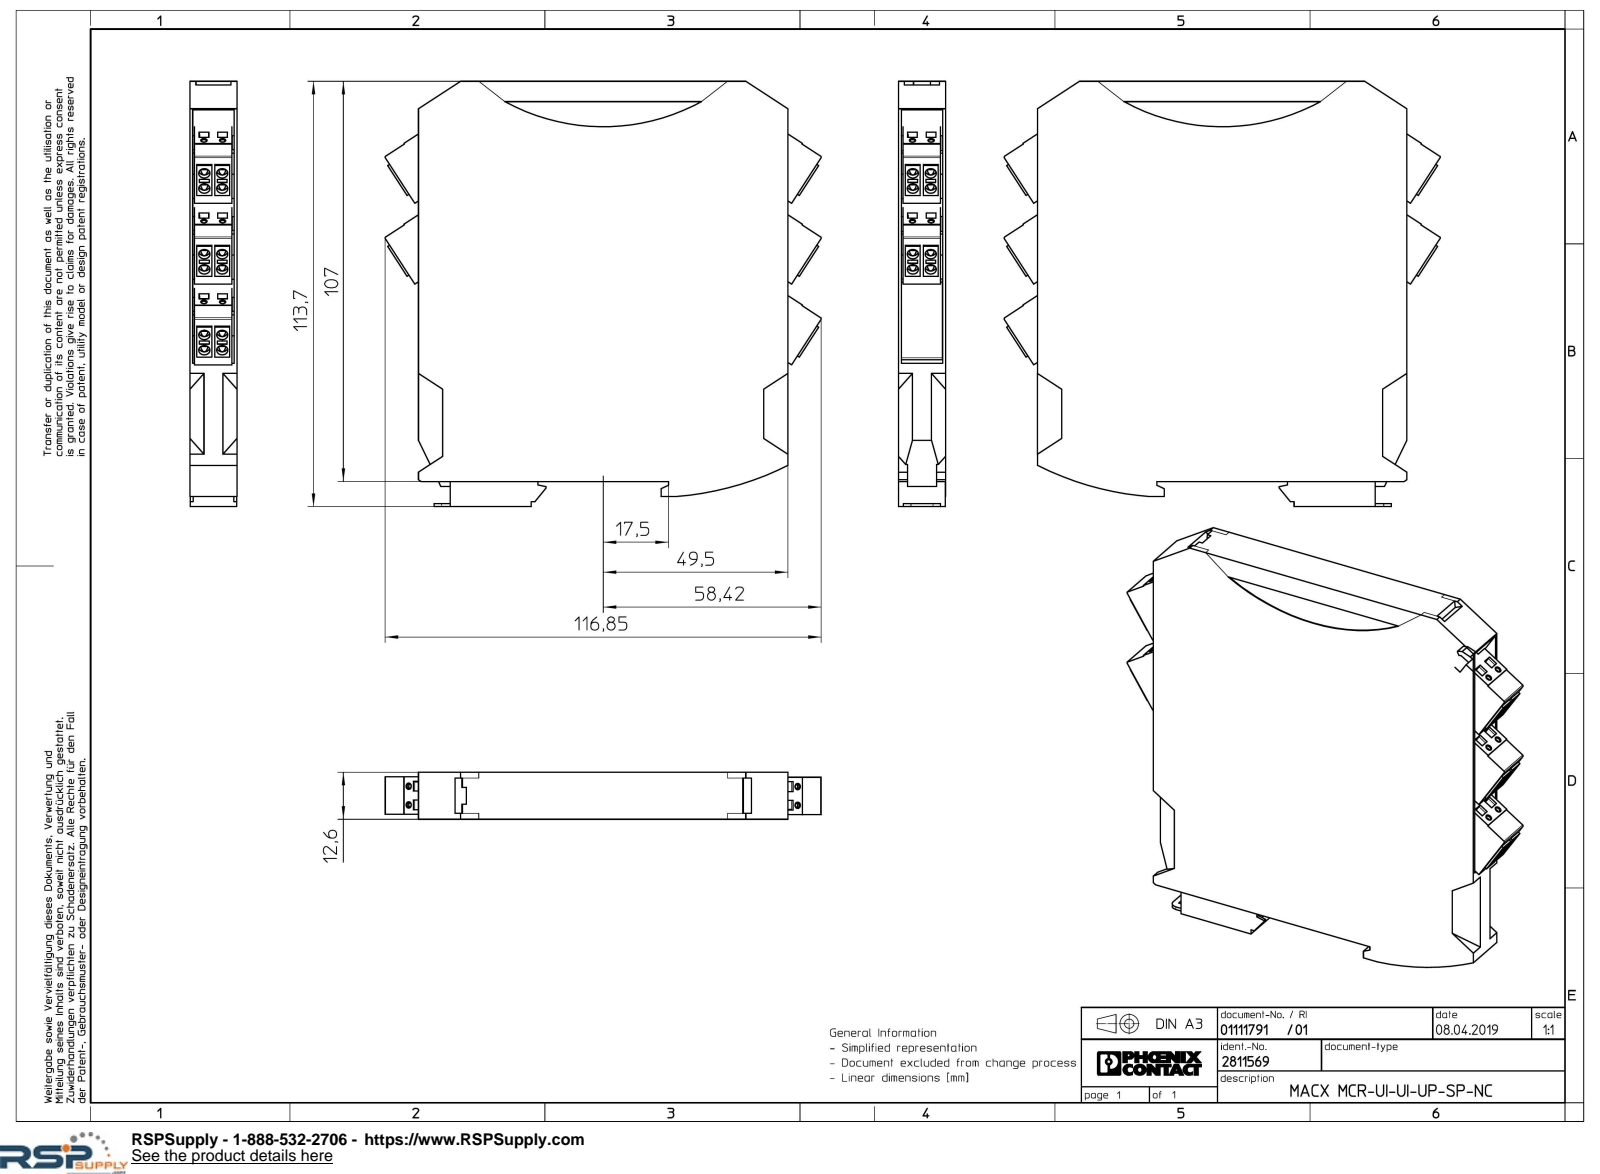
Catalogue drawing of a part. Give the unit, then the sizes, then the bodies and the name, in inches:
Units: inches
Overall size (bounding box): 4.6 × 4.476 × 0.496
Round holes (diameter × count): ⌀0.118 ×30, ⌀0.051 ×10, ⌀0.06 ×10
Round bosses / shafts (diameter × count): ⌀0.11 ×6
Partial cylindrical surfaces — rounded edges, fillets, slot ends (radius × count): R0.049 ×20, R0.118 ×13, R0.114 ×10, R0.055 ×6, R0.012 ×5, R0.079 ×2, R0.02 ×1, R0.059 ×1
Main face-to-face distances: 0.496, 0.049, 0.03, 0.467, 0.447, 0.02, 0.417, 0.394, 0.024, 0.713
Hole centre spacings: 0.189, 0.197, 0.199, 0.713, 0.191, 0.269, 0.713, 0.048
Volume: 8.107 in³ · Surface area: 66.4 in²
Bodies: 7 solids, 1160 faces (876 planar, 194 cylindrical, 90 other)
Part name (STEP PRODUCT): MACX_12.5-SOCKEL_159_160_GY7042-select; TVFKC_1.5_2-ST_GY-select; ME_MAX_B-12.5_GY7042-select; TVFKC_1.5_2-ST_GY7035-select (+1 more)
STEP written by: Creo Elements/Direct Modeling 20.1A 29-Sep-2018 (C) Parametric Technology GmbH (AUTOMOTIVE_DESIGN)
